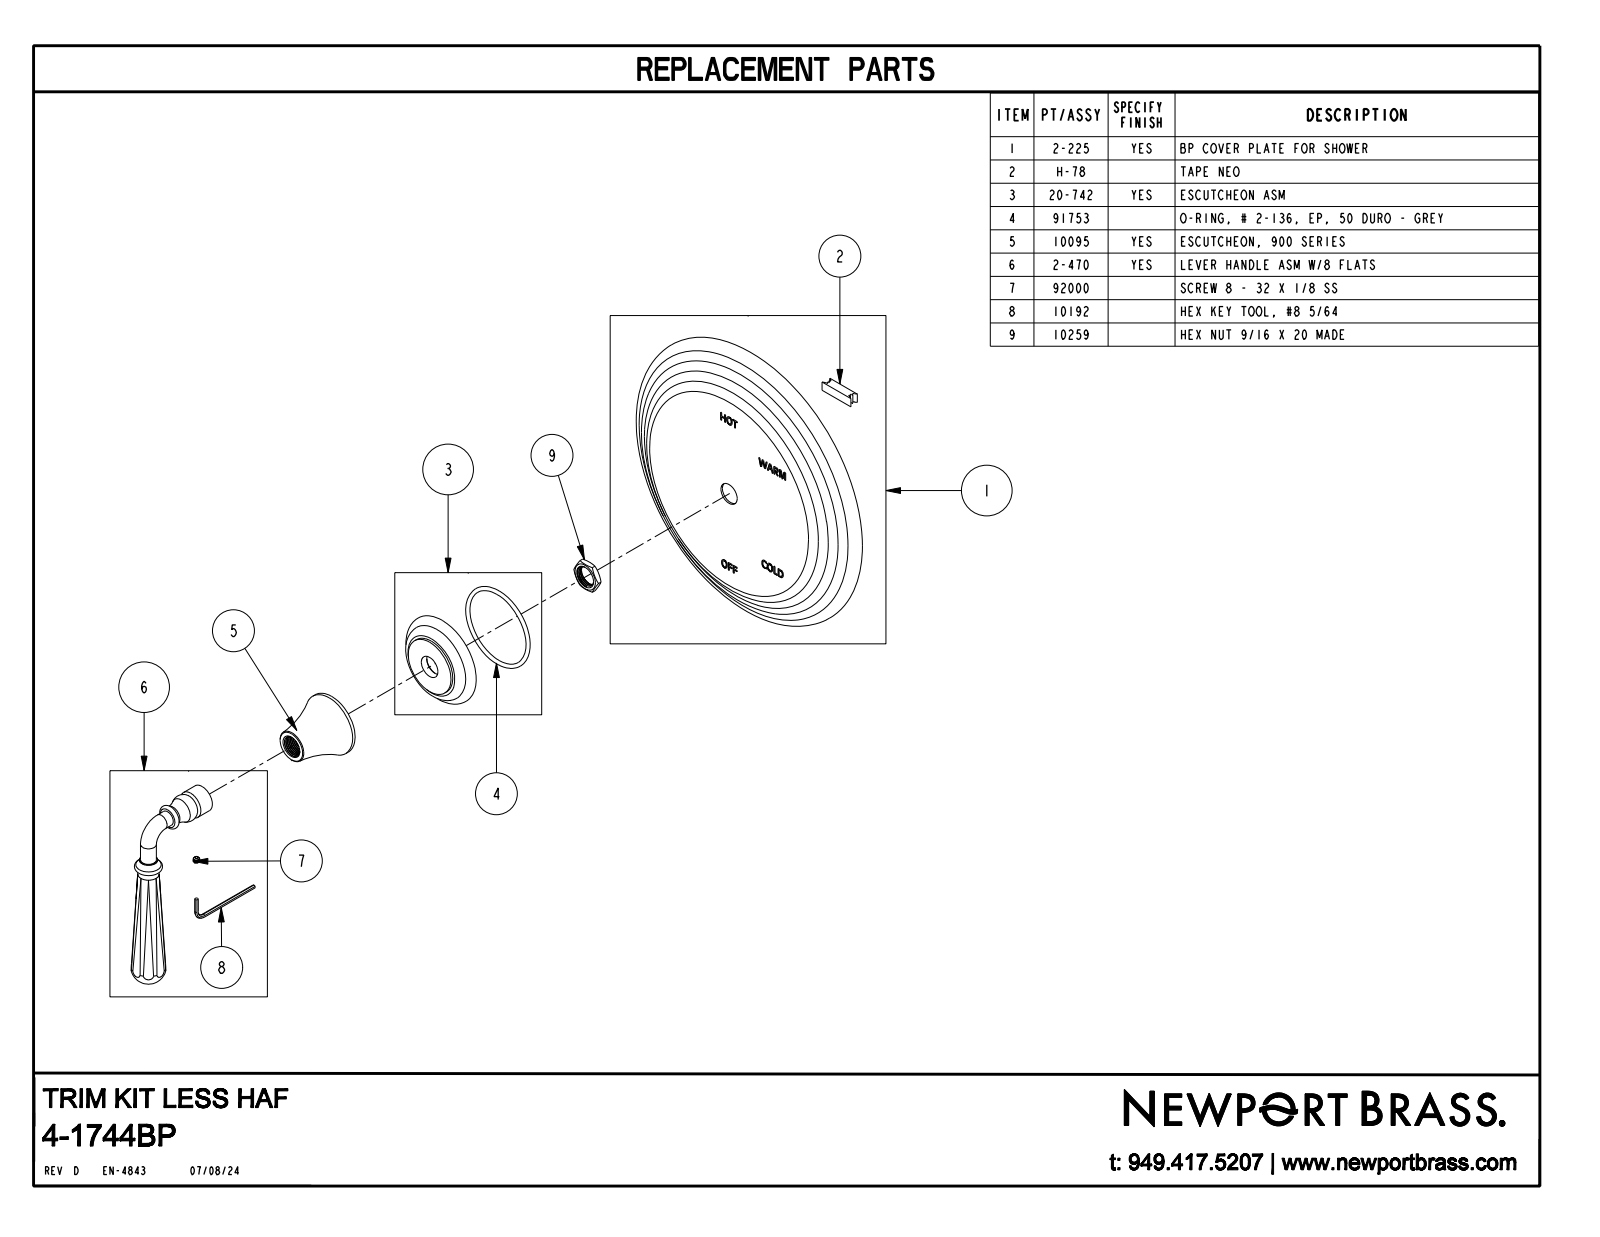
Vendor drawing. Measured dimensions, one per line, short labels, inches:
name: 4-1744BP
written by: CREO PARAMETRIC BY PTC INC, 2018400 (CONFIG_CONTROL_DESIGN)
unit: in
bodies: 1 solid, 277 faces (137 planar, 14 cylindrical, 126 other)
size: 8.432 × 7.75 × 4.849
volume: 32.39 in³; area: 119.5 in²
bosses: 2× ⌀0.39, 1× ⌀1.625, 1× ⌀0.705, 1× ⌀0.525, 1× ⌀0.475, 1× ⌀0.4
face distances: 0.754, 1.775, 2.529, 2.559, 1.805, 0.03, 0.75, 1.779, 1.809, 3.759
